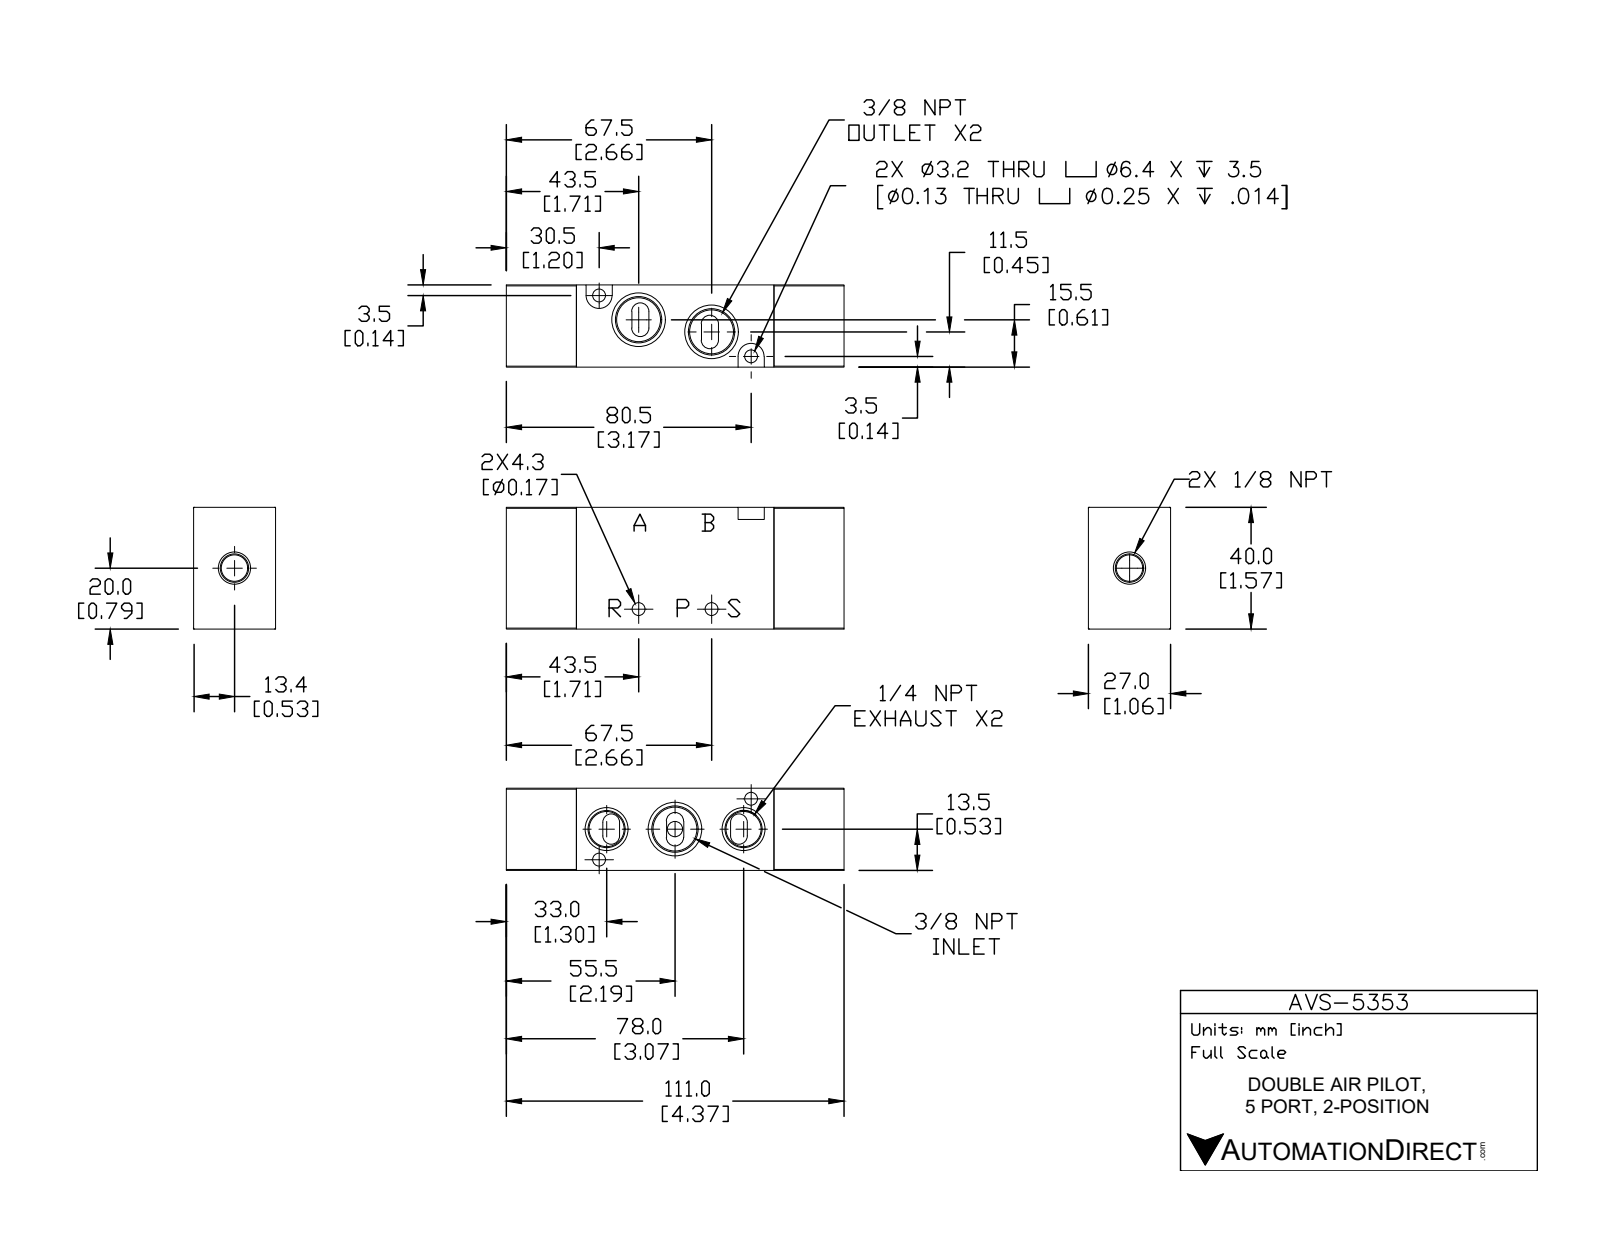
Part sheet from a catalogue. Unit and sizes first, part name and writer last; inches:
Units: inches
Overall size (bounding box): 4.37 × 1.575 × 1.063
Round holes (diameter × count): ⌀0.169 ×4, ⌀0.199 ×1
Partial cylindrical surfaces — rounded edges, fillets, slot ends (radius × count): R0.111 ×6, R0.012 ×4, R0.108 ×4, R0.169 ×2
Main face-to-face distances: 1.063, 1.575, 2.559, 0.906, 3.465, 4.37, 0.63, 0.461, 1.114, 0.945
Hole centre spacings: 1.06, 0.945, 2.12
Volume: 6.621 in³ · Surface area: 40.66 in²
Bodies: 3 solids, 111 faces (47 planar, 36 cylindrical, 28 other)
Part name (STEP PRODUCT): AVS-5353
STEP written by: SolidWorks 2015 (CONFIG_CONTROL_DESIGN)
